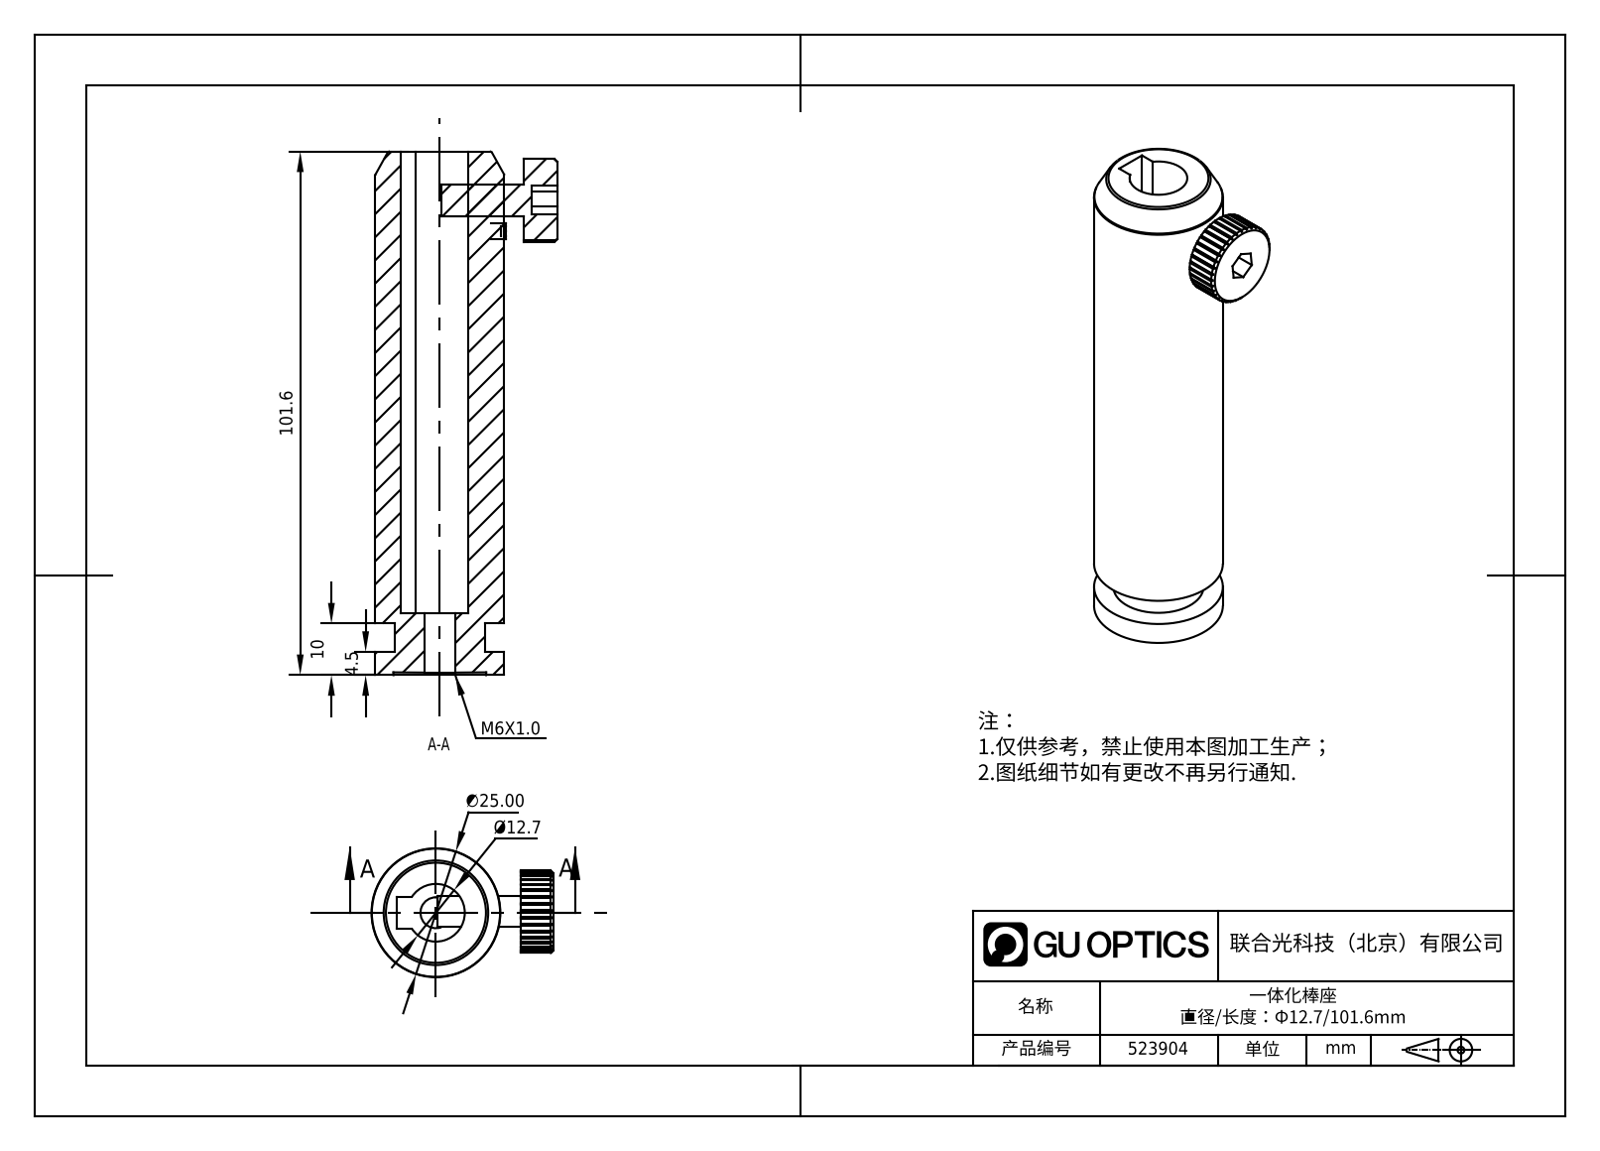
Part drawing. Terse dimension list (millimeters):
name: 523904
written by: SolidWorks 2016 (AUTOMOTIVE_DESIGN)
unit: mm
bodies: 0 solids, 163 faces (99 planar, 52 cylindrical, 12 other)
size: 101.6 × 35.27 × 25
holes: 1× ⌀6, 1× ⌀11.19
bosses: 1× ⌀25, 1× ⌀17.5, 1× ⌀6, 1× ⌀3
rounds: 1× R8
face distances: 6.25, 5.5, 4.5, 10, 101.6, 97.1, 91.6, 24.02, 30.42, 6.4
